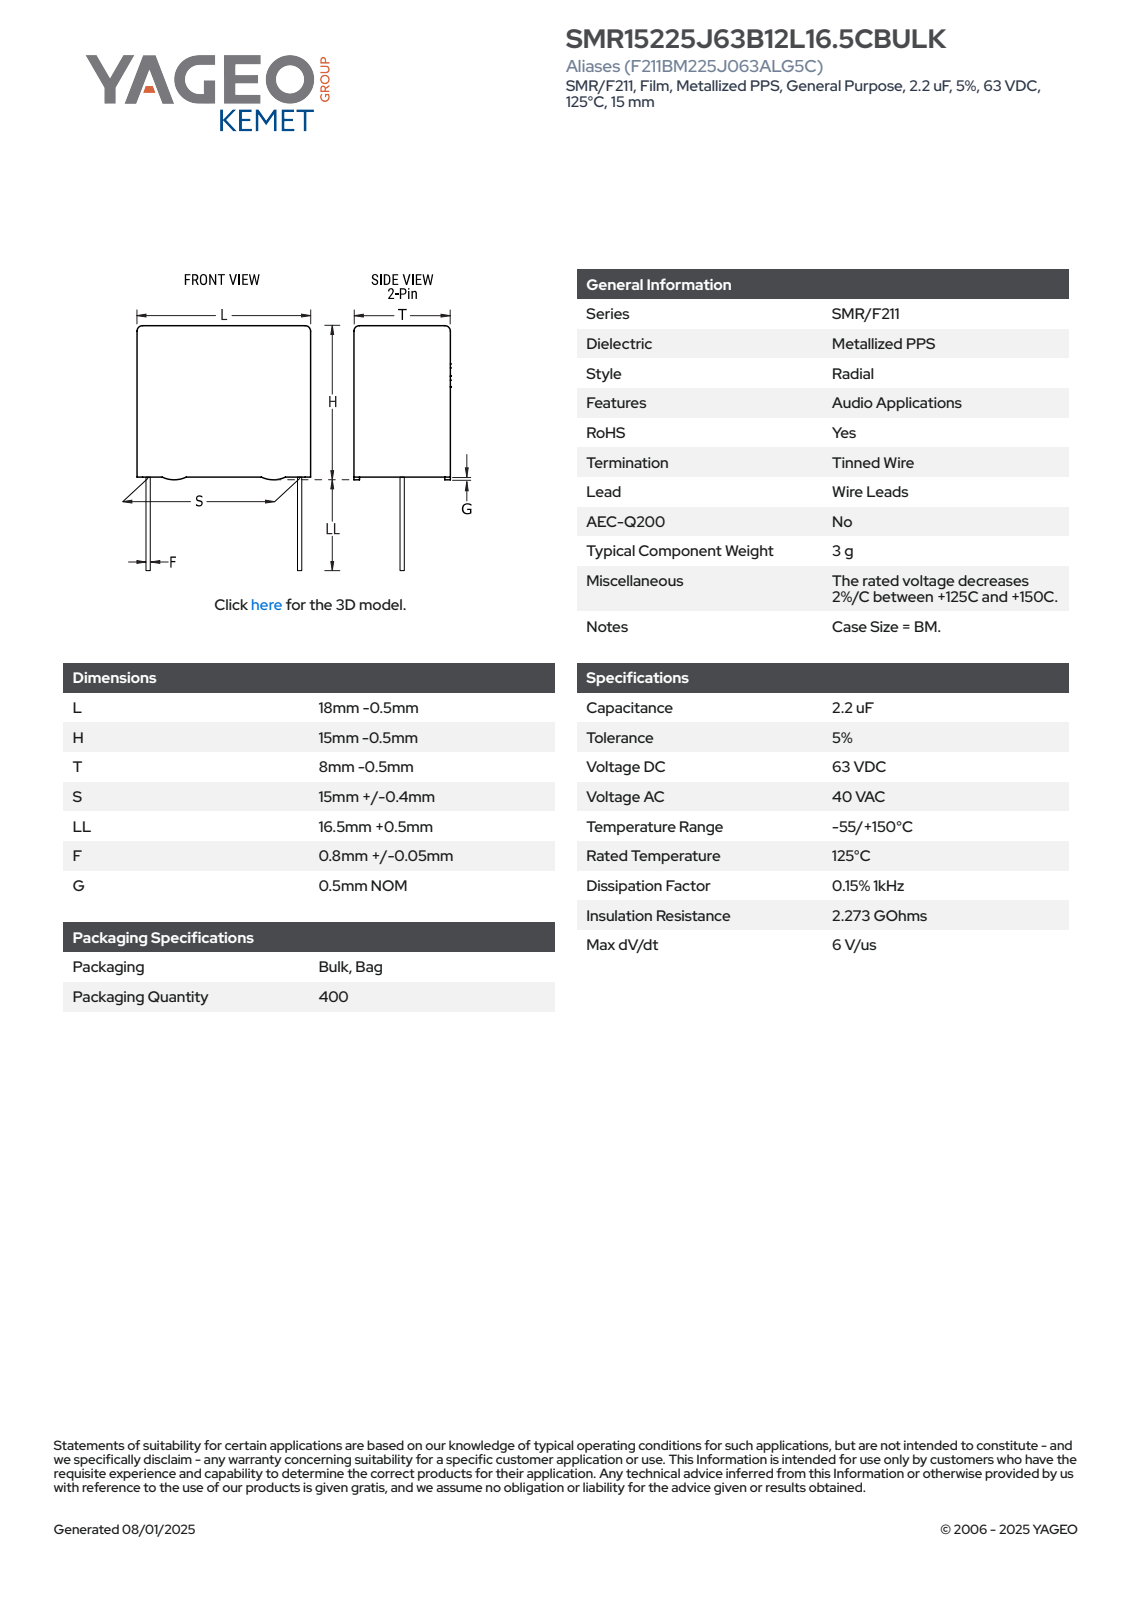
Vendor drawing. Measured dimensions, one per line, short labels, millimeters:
name: CFR_RBG_18X15X8_L17.5H14.5T7.5S15LL17F0.85G0.5
written by: SolidWorks 2021 (AUTOMOTIVE_DESIGN)
unit: mm
bodies: 4 solids, 89 faces (81 planar, 8 cylindrical, 0 other)
size: 31.5 × 17.5 × 7.5
volume: 1 857 mm³; area: 1 091 mm²
bosses: 2× ⌀0.85
rounds: 4× R0.5
face distances: 7.5, 14, 17.5, 0.43, 7.07, 0.5, 14.5, 6.64, 17, 31.5
